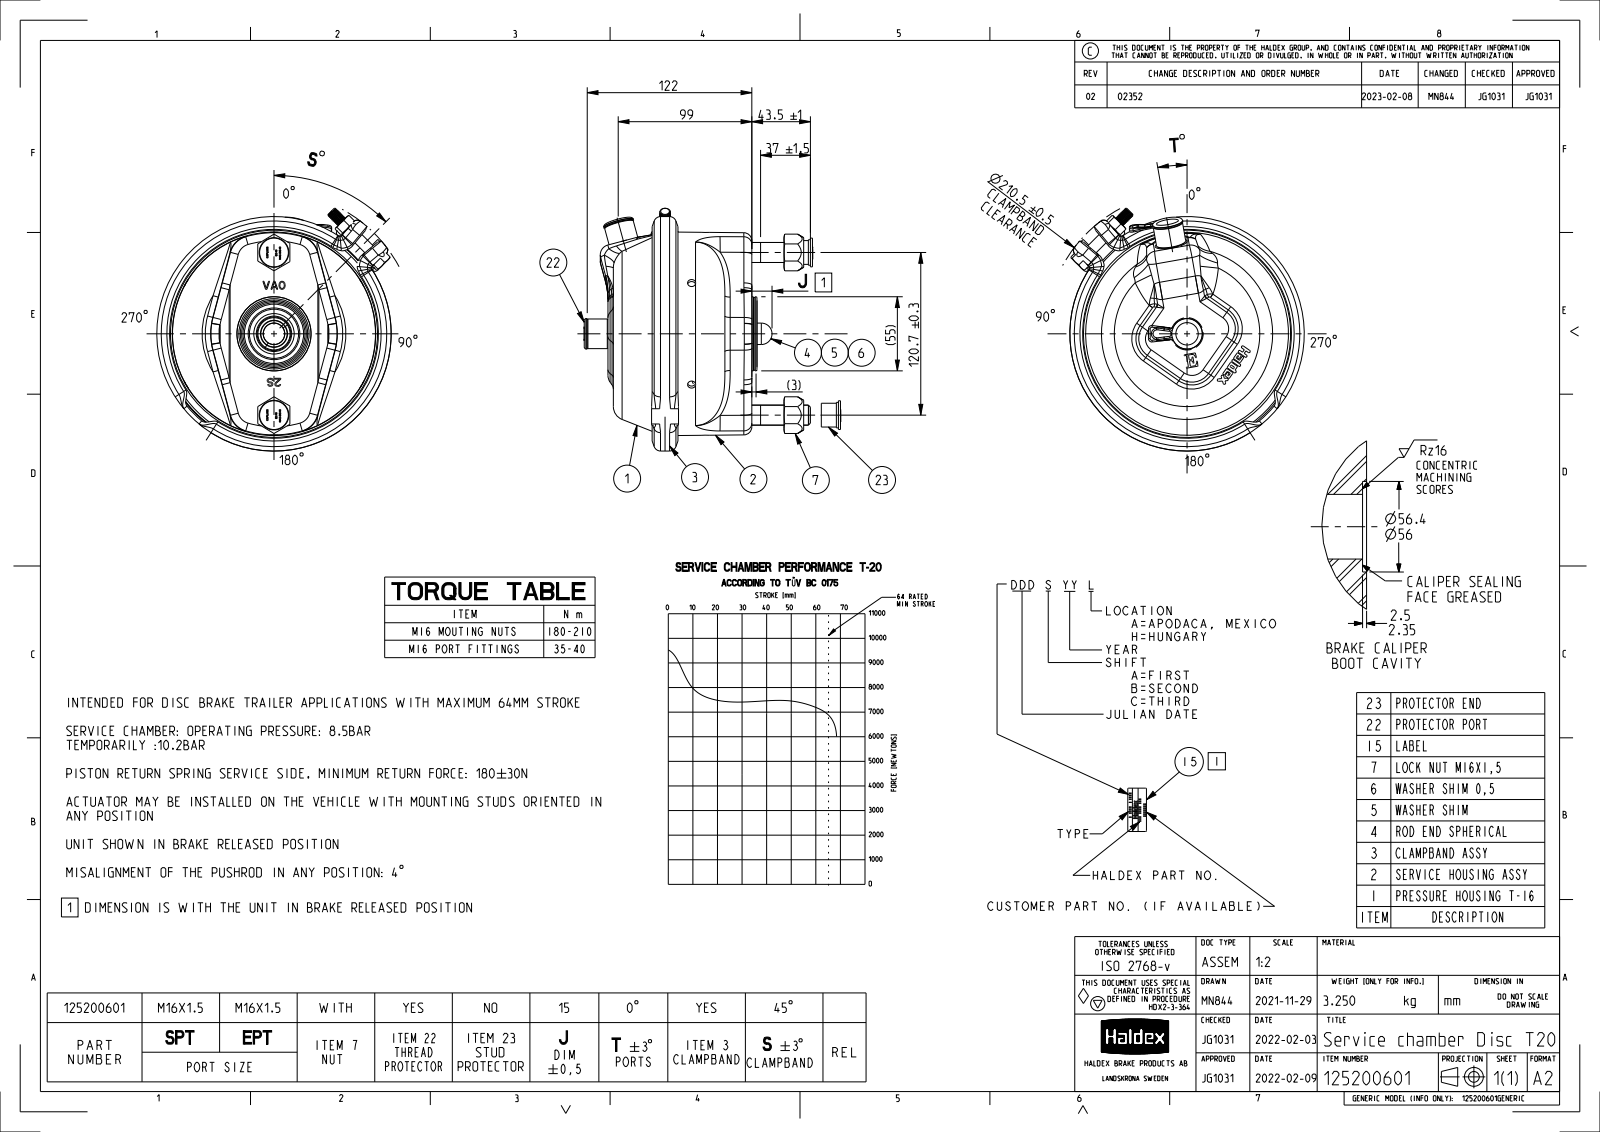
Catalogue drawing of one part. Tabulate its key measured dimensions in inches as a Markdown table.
| quantity | value |
| --- | --- |
| part name | 9956019; 9999406; 9956007_ASM; 9960004 (+8 more) |
| STEP written by | CREO PARAMETRIC BY PTC INC, 2018500 (AUTOMOTIVE_DESIGN) |
| units | inches |
| bodies | 25 solids, 3458 faces (2122 planar, 477 cylindrical, 859 other) |
| overall size | 7.092 × 7.082 × 6.684 |
| volume | 33.3 in³ |
| surface area | 591 in² |
| round holes (diameter × count) | 0.236 × 3, 0.354 × 2, 0.492 × 2, 0.571 × 2, 0.591 × 2, 0.625 × 2, 0.648 × 2, 0.24 × 1, 0.315 × 1, 0.394 × 1, 0.402 × 1, 0.531 × 1 |
| round bosses / shafts (diameter × count) | 0.63 × 3, 0.894 × 2, 0.866 × 2, 0.84 × 2, 0.745 × 2, 0.695 × 2, 0.635 × 2, 0.585 × 2 |
| partial cylindrical surfaces (radius × count) | 0.01 × 26, 0.236 × 20, 0.025 × 19, 0.004 × 17, 0.005 × 16, 0.05 × 14, 0.011 × 12, 0.022 × 11 |
| main face-to-face distances | 0.118, 3.827, 0.236, 0.354, 3.472, 3.709, 3.591, 0.105, 3.945, 0.157 |
| hole center spacings | 2.376, 1.146, 1.23, 3.606, 4.752 |
